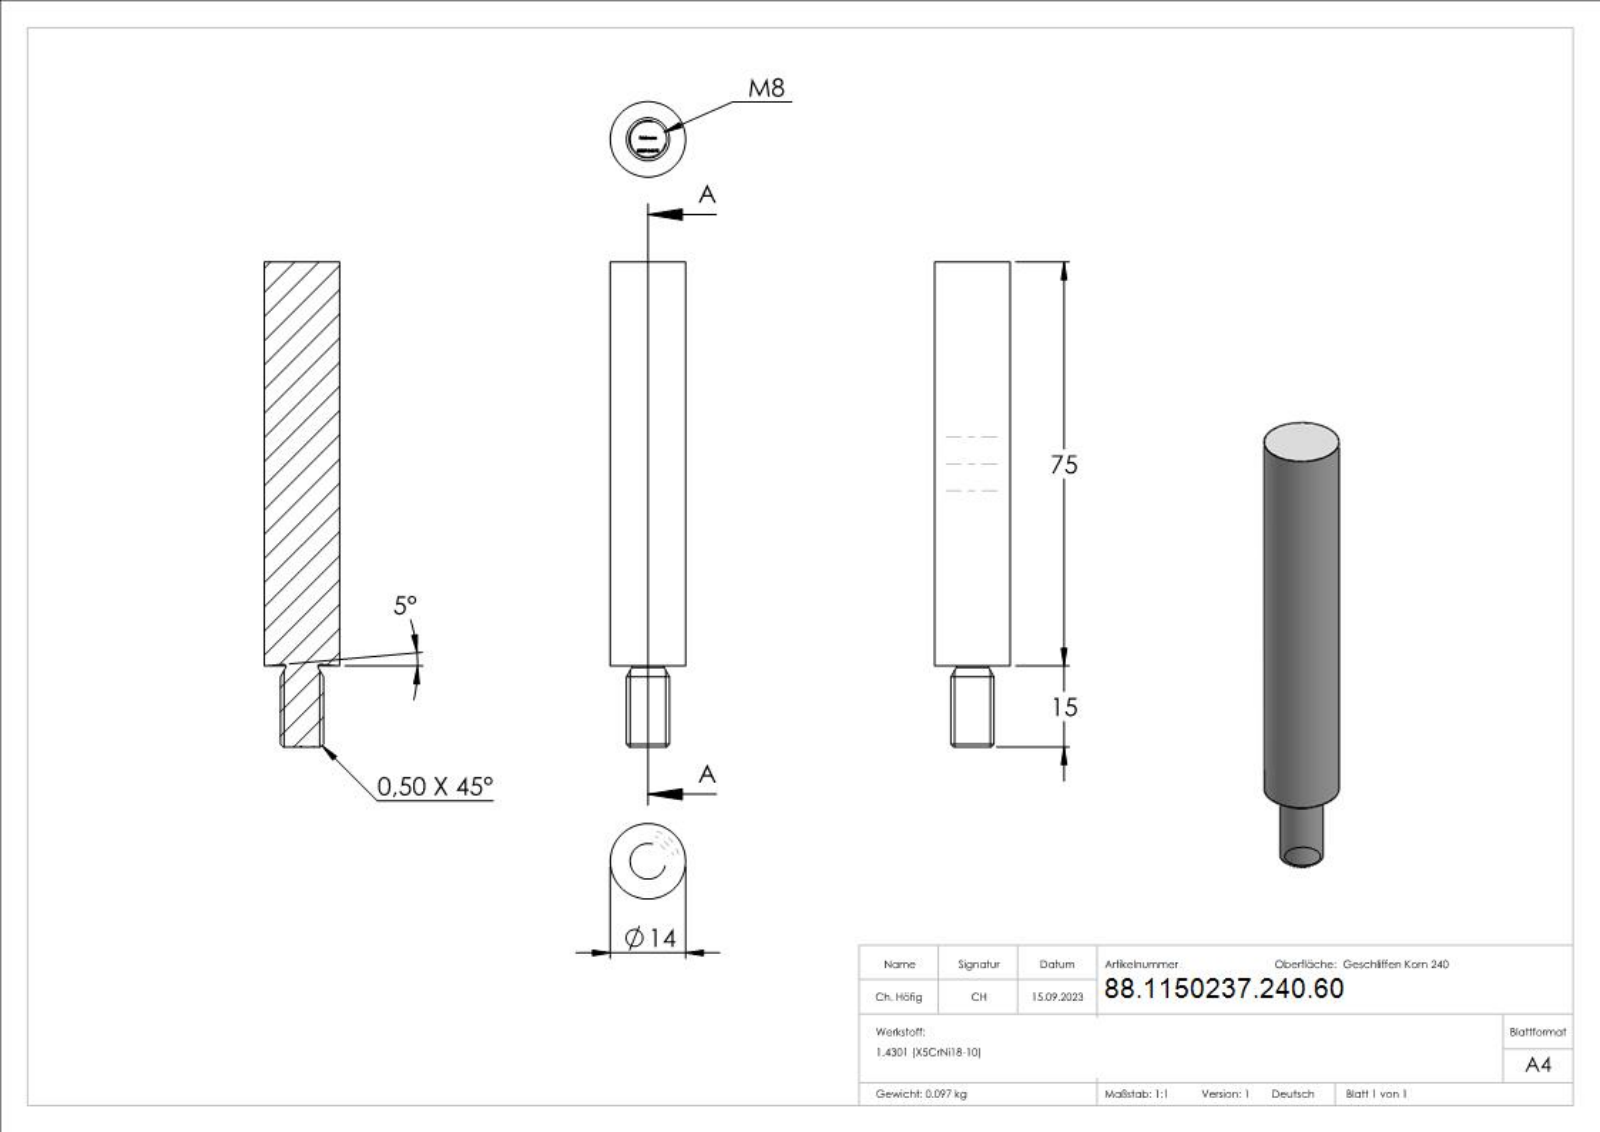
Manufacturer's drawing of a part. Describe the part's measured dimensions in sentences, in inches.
The part is named "50237-240-60". Its 3-D file was written by "SolidWorks 2018 (CONFIG_CONTROL_DESIGN)". It is 1 solid with 259 faces: 135 planar, 2 cylindrical and 122 other. Overall it measures 2.953 by 0.551 by 0.551 inches. Its volume is 0.607 cubic inches and its surface area 5.186 square inches. Round bosses or shafts: 1 of diameter 0.551, 1 of diameter 0.315. The main face-to-face distances are 2.953, 2.949, 0.059, 0.022, 0.094, 0.021, 0.014, 0.024, 0.096, 0.057.
